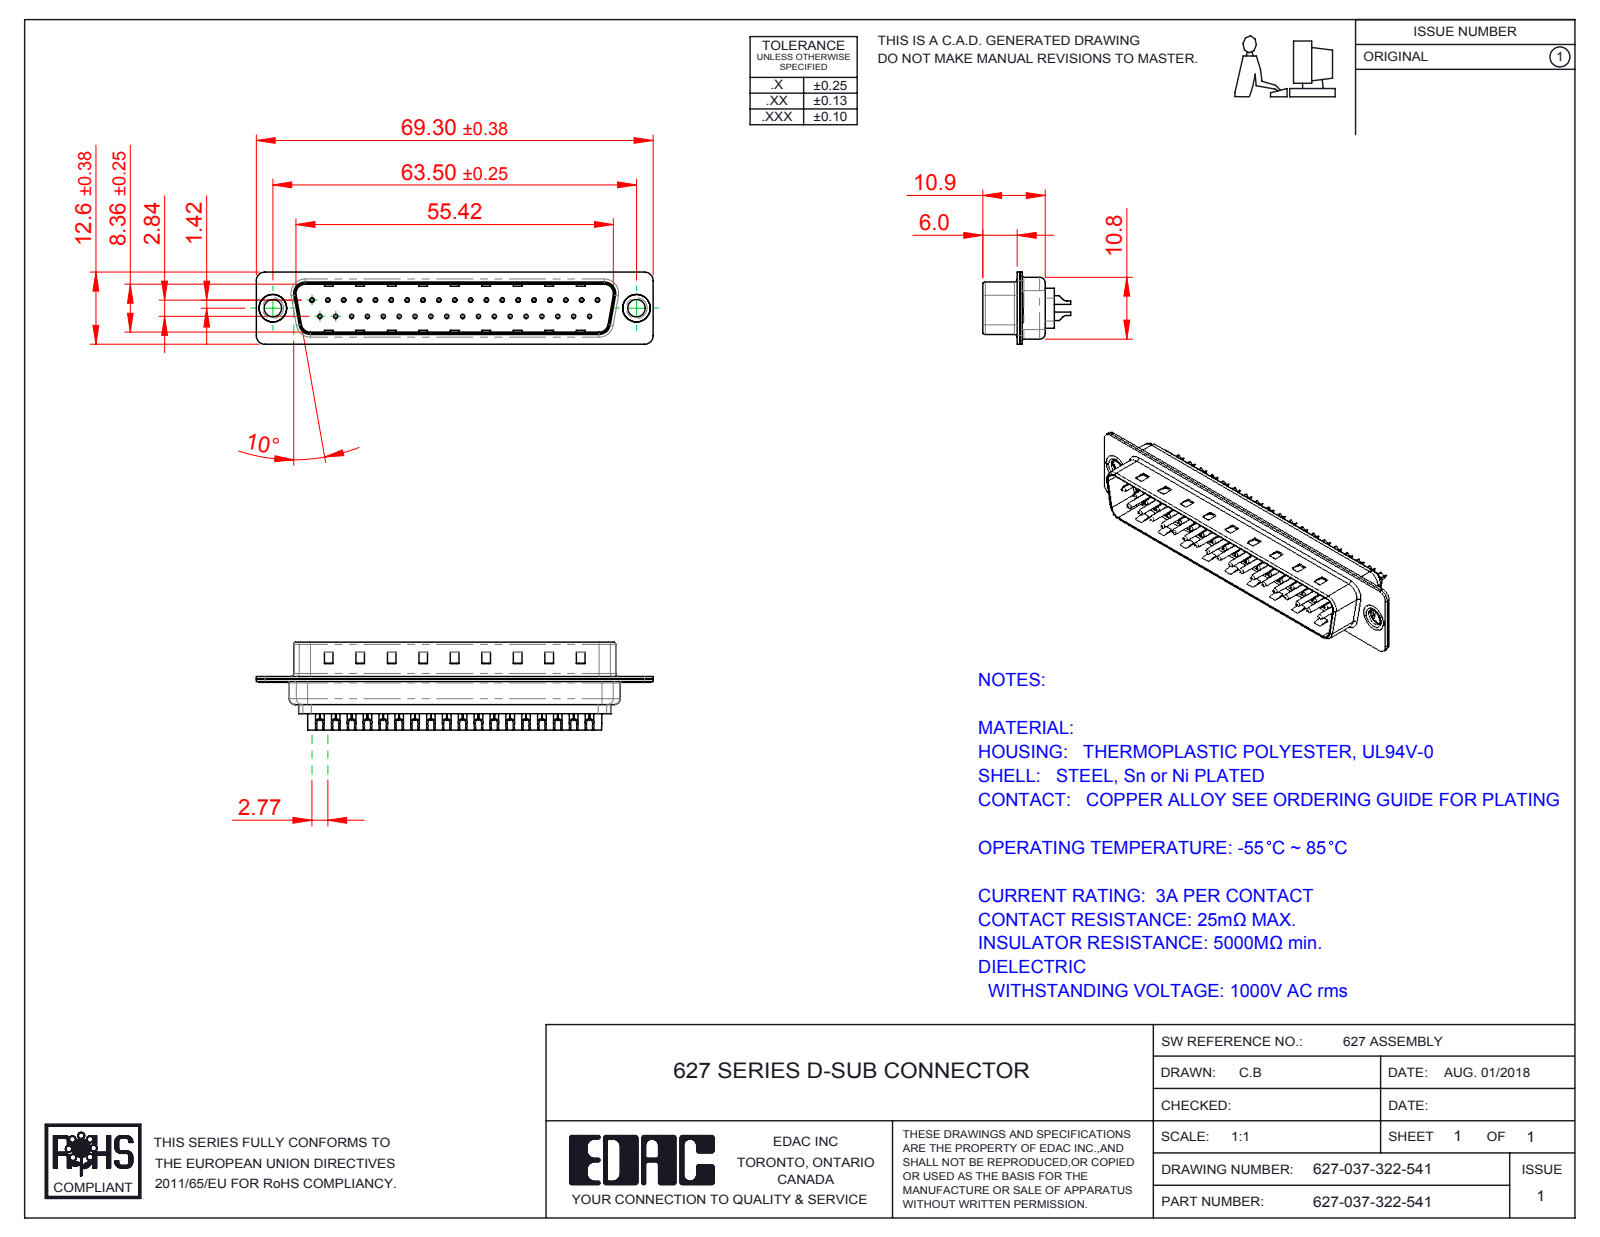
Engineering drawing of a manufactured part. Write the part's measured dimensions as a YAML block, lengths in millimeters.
part_name: "627 Shell Front_37 Contacts; 627 Shell Rear_37 Contacts; 627 Contact Row 2_22L; 627 Thru Hole Rivet (+3 more)"
step_written_by: "SolidWorks 2016 (CONFIG_CONTROL_DESIGN)"
units: millimeters
bodies: {solids: 42, faces: 2754, planar: 721, cylindrical: 1198, other: 835}
overall_size: [69.3, 15.35, 12.6]
volume: 3636
surface_area: 10612
round_holes:
  - {diameter: 0.35, count: 37}
  - {diameter: 1.1, count: 37}
  - {diameter: 1.6, count: 37}
  - {diameter: 3.05, count: 2}
  - {diameter: 4, count: 2}
  - {diameter: 4.8, count: 2}
round_bosses_or_shafts:
  - {diameter: 2, count: 37}
  - {diameter: 1.5, count: 37}
  - {diameter: 0.75, count: 37}
  - {diameter: 5, count: 2}
  - {diameter: 4.9, count: 2}
  - {diameter: 3.55, count: 2}
partial_cylinders:
  - {radius: 1.5, count: 16}
  - {radius: 2, count: 12}
  - {radius: 0.5, count: 8}
  - {radius: 1.6, count: 8}
  - {radius: 1, count: 6}
  - {radius: 0.25, count: 4}
  - {radius: 0.6, count: 4}
  - {radius: 0.65, count: 4}
face_to_face_distances: [0.4, 0.82, 9.58, 0.45, 8.76, 1.5, 0.9, 1.4, 6.05, 0.5]
hole_center_spacings: [3.16, 2.77, 5.54, 8.31, 5.04, 10.1, 11.08, 12.78]
